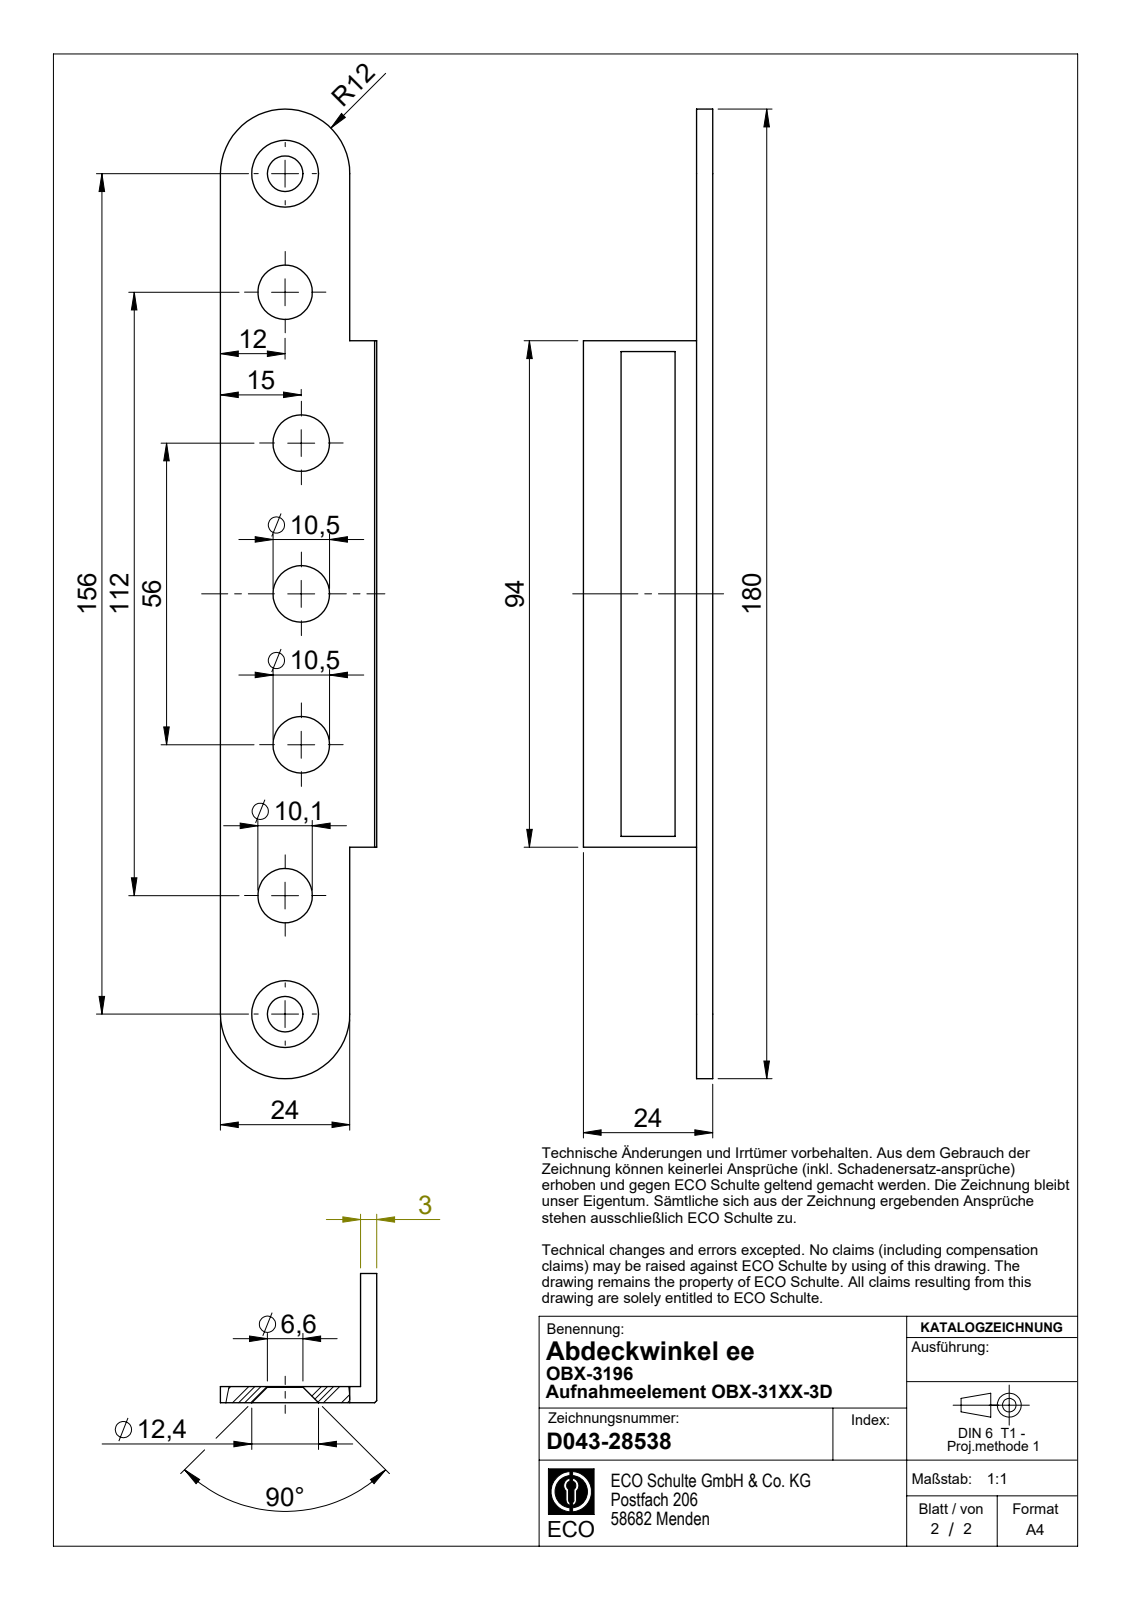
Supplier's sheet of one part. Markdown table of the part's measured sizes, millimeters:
| quantity | value |
| --- | --- |
| part name | OBX-3196-ee_D043-28538 |
| STEP written by | SolidWorks 2020 (AUTOMOTIVE_DESIGN) |
| units | millimeters |
| bodies | 1 solid, 35 faces (15 planar, 16 cylindrical, 4 other) |
| overall size | 180 × 29 × 24 |
| volume | 15 523 mm³ |
| surface area | 12 963 mm² |
| round holes (diameter × count) | 10.5 × 3, 6.6 × 2, 10.1 × 2 |
| partial cylindrical surfaces (radius × count) | 12 × 2 |
| main face-to-face distances | 3, 7, 17, 26, 29, 24, 21, 4, 10, 14 |
| hole center spacings | 22, 28, 28.16, 50.09, 56.08, 78.06, 84.05, 106.04 |
